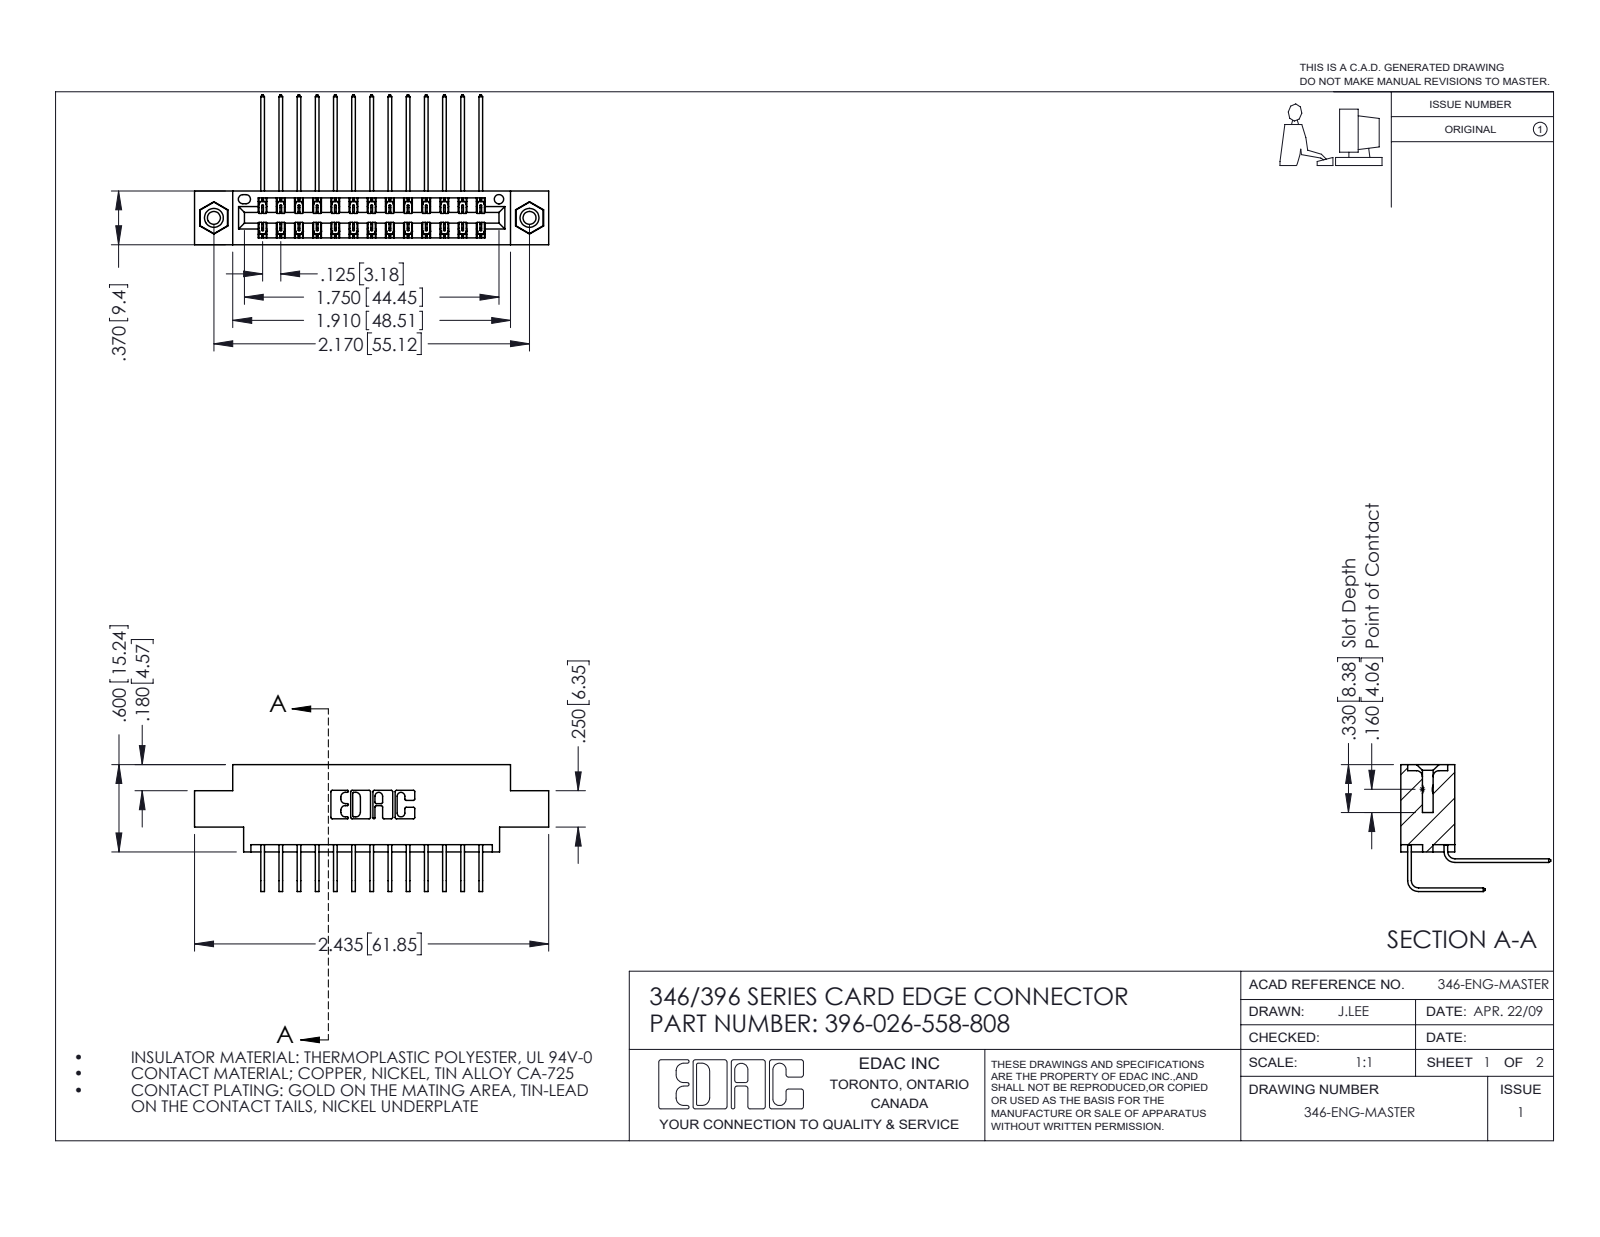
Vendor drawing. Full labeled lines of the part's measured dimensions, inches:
Part name (STEP PRODUCT): 396-026-558-808; 345-292-001_558 Tail - 2; 346 Part_0.170 Offset - 0.156 Dia-TI; 345-250-001_345-250-003-102 (+1 more)
STEP written by: SolidWorks 2016 (CONFIG_CONTROL_DESIGN)
Units: inches
Bodies: 29 solids, 1590 faces (1074 planar, 500 cylindrical, 16 other)
Overall size (bounding box): 2.435 × 1.03 × 0.873
Volume: 0.354 in³ · Surface area: 13.06 in²
Round holes (diameter × count): ⌀0.089 ×2, ⌀0.125 ×2, ⌀0.156 ×2, ⌀0.064 ×1
Round bosses / shafts (diameter × count): ⌀0.155 ×2
Partial cylindrical surfaces — rounded edges, fillets, slot ends (radius × count): R0.006 ×39, R0.01 ×22, R0.007 ×6, R0.031 ×6, R0.026 ×3, R0.014 ×2, R0.022 ×2, R0.024 ×2
Main face-to-face distances: 0.048, 0.322, 0.25, 0.37, 0.025, 0.072, 0.298, 0.222, 0.275, 0.148
Hole centre spacings: 0.246, 1.964, 2.17
